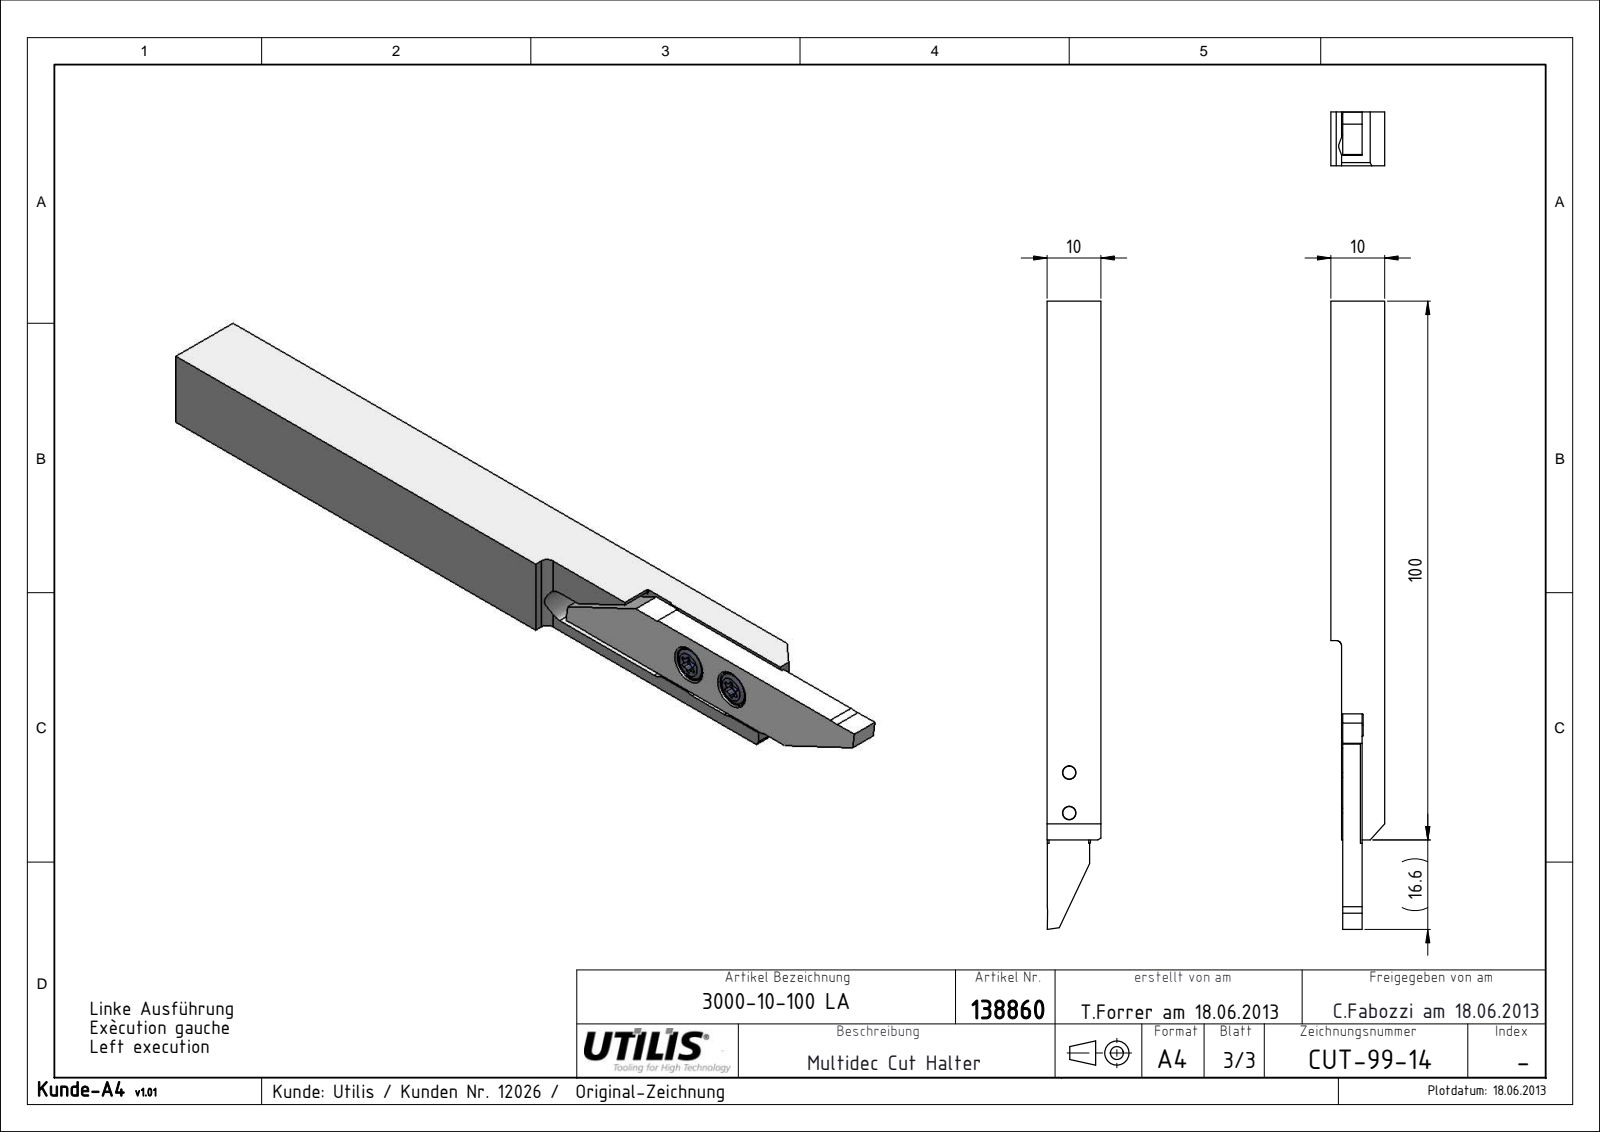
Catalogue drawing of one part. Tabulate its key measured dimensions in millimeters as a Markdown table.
| quantity | value |
| --- | --- |
| part name | CUT-99-14 |
| STEP written by | SolidWorks 2016 (AUTOMOTIVE_DESIGN) |
| units | millimeters |
| bodies | 1 solid, 46 faces (34 planar, 8 cylindrical, 4 other) |
| overall size | 116.6 × 10 × 10 |
| volume | 9 410 mm³ |
| surface area | 4 619 mm² |
| partial cylindrical surfaces (radius × count) | 2.1 × 4, 10 × 2, 1 × 1 |
| main face-to-face distances | 10, 2.2, 7.8, 8, 4.2, 3.8, 5.8, 3.6, 9.95, 2 |
